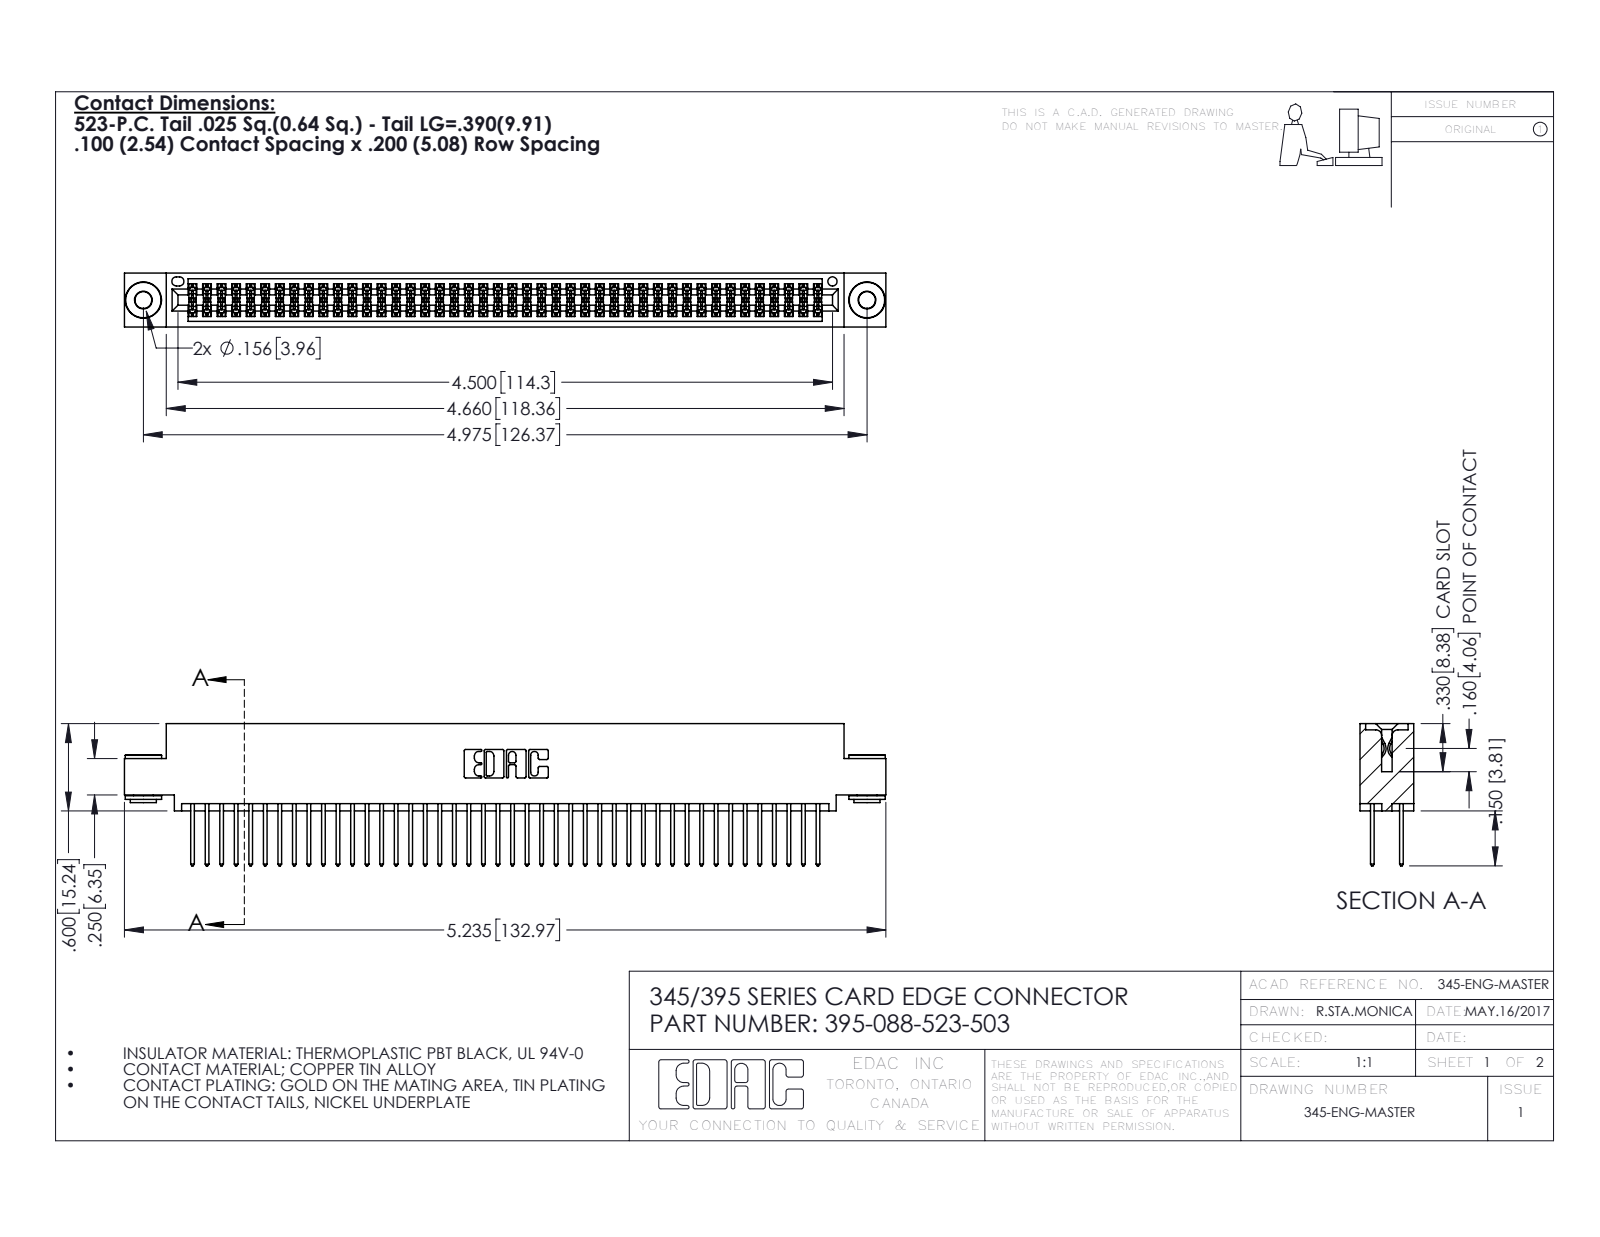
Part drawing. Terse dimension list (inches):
name: 345 Part_0.110 Offset - 0.156 Dia-TH; 345-250-002_345-250-002-102; 345-292-001_345-293-123; 395-088-523-503
written by: SolidWorks 2016 (CONFIG_CONTROL_DESIGN)
unit: in
bodies: 91 solids, 4568 faces (2998 planar, 1562 cylindrical, 8 other)
size: 5.235 × 0.977 × 0.37
volume: 0.797 in³; area: 31.7 in²
holes: 2× ⌀0.116, 2× ⌀0.156, 1× ⌀0.064
bosses: 2× ⌀0.25, 2× ⌀0.18, 2× ⌀0.136
rounds: 132× R0.006, 88× R0.01, 22× R0.01, 6× R0.007, 6× R0.031, 3× R0.026, 2× R0.014, 2× R0.019
face distances: 0.072, 0.298, 0.2, 0.025, 0.098, 0.272, 0.37, 0.225, 0.175, 0.149
hole spacings: 0.27, 4.739, 4.975
